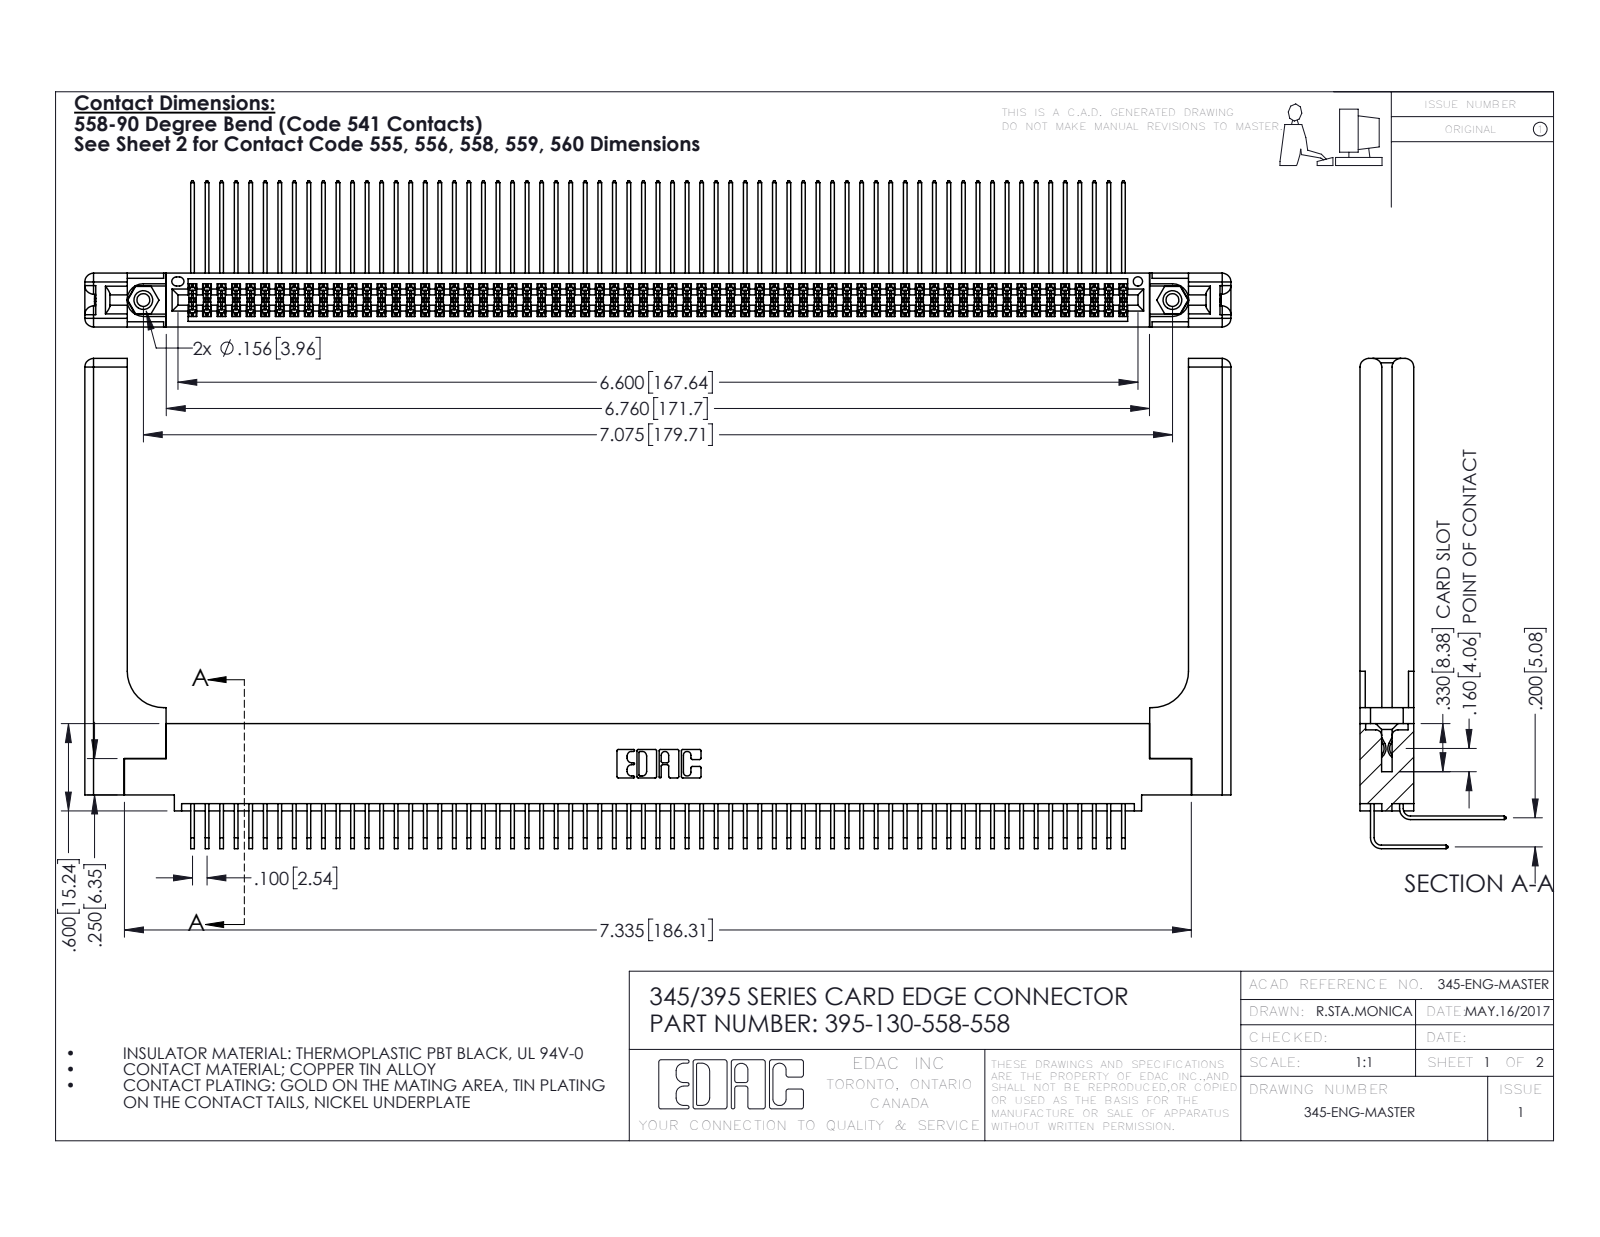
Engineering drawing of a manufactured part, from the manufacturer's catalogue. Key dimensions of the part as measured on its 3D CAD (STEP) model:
Part name (STEP PRODUCT): 395-130-558-558; 345-220-058_345-220-058; 345-292-001_558 Tail - 2; 345-250-001_345-250-001-102 (+2 more)
STEP written by: SolidWorks 2016 (CONFIG_CONTROL_DESIGN)
Units: inches
Bodies: 135 solids, 7146 faces (4782 planar, 2304 cylindrical, 60 other)
Overall size (bounding box): 7.879 × 3.369 × 1.005
Volume: 1.758 in³ · Surface area: 60.72 in²
Round holes (diameter × count): ⌀0.089 ×2, ⌀0.125 ×2, ⌀0.156 ×2, ⌀0.064 ×1
Round bosses / shafts (diameter × count): ⌀0.155 ×2
Partial cylindrical surfaces — rounded edges, fillets, slot ends (radius × count): R0.006 ×196, R0.01 ×22, R0.06 ×16, R0.007 ×6, R0.031 ×6, R0.026 ×3, R0.014 ×2, R0.019 ×2
Main face-to-face distances: 0.072, 0.298, 0.37, 0.2, 0.098, 0.272, 0.025, 0.225, 0.025, 0.148
Hole centre spacings: 0.27, 6.839, 7.075
